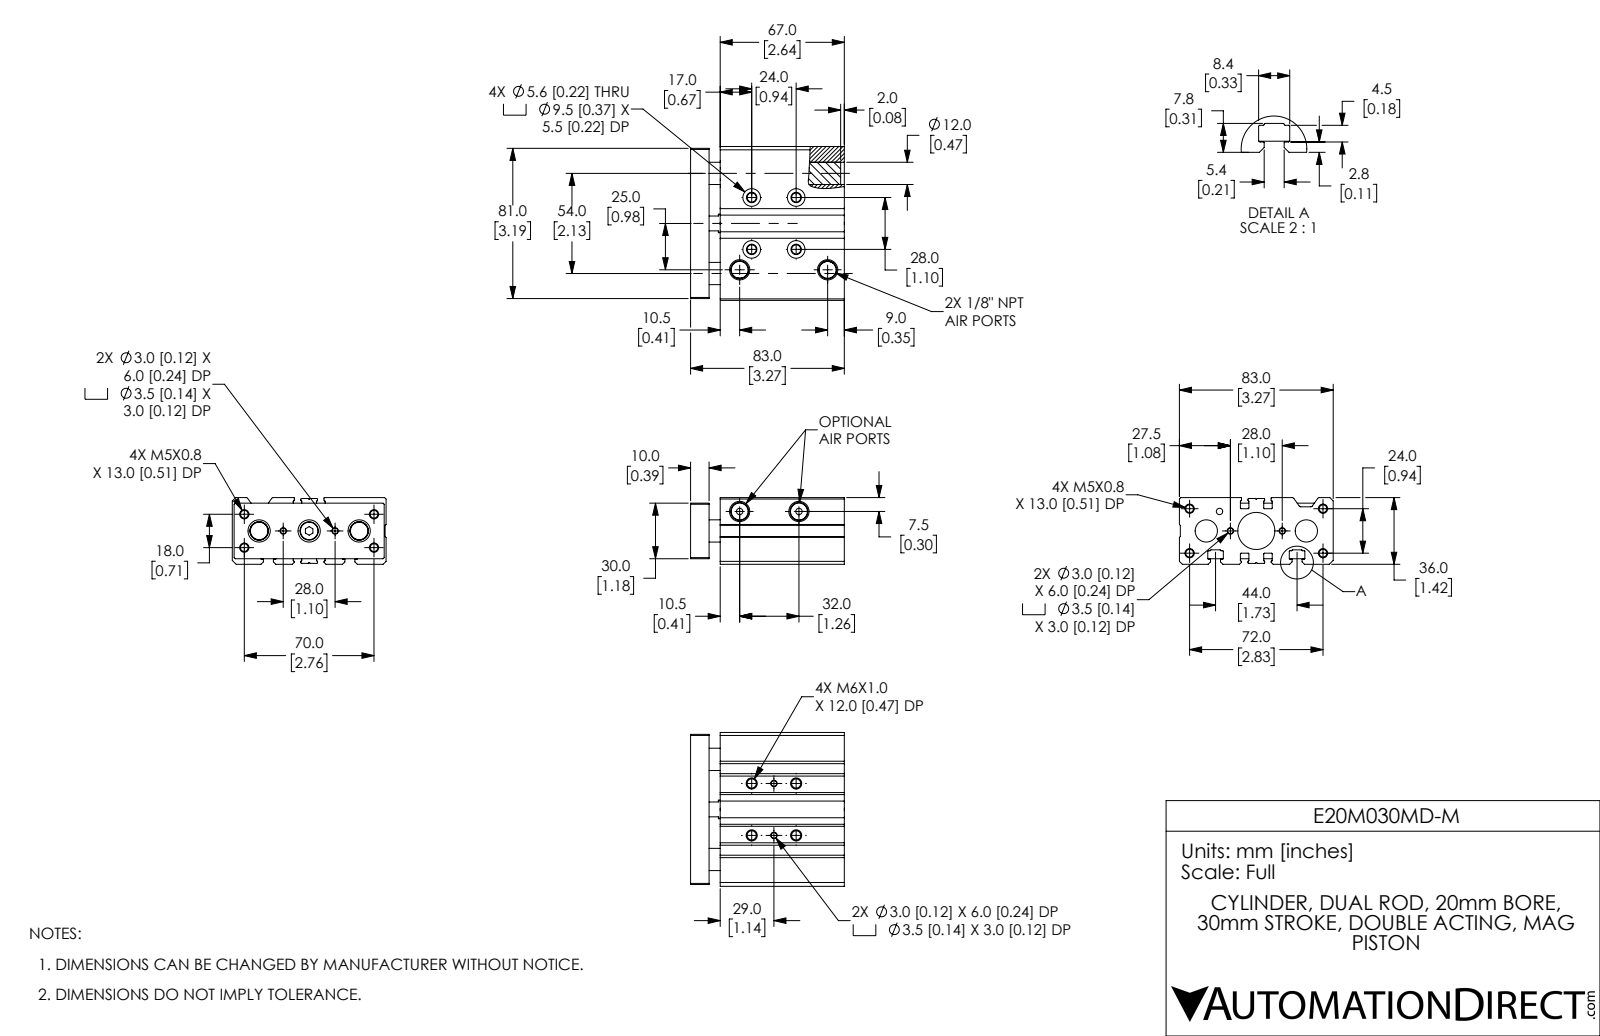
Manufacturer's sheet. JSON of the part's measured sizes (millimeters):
{"part_name": "E20M030MD-M_BODY; E20M030MD-M_ENDPLATE; E20M030MD-M", "step_written_by": "SolidWorks 2019 (CONFIG_CONTROL_DESIGN)", "units": "millimeters", "bodies": {"solids": 5, "faces": 404, "planar": 128, "cylindrical": 182, "other": 94}, "overall_size": [83, 83, 36], "volume_mm3": 189562, "surface_area_mm2": 60022, "round_holes": [[4.13, 8], [3, 4], [3.5, 4], [4.92, 4], [5.6, 4], [9.5, 4], [6, 3], [12, 3], [3.43, 2], [9.91, 2], [3.43, 1], [12, 1]], "round_bosses_or_shafts": [[10, 1], [9.91, 1]], "partial_cylinders_radius": [[0.4, 20], [0.2, 18], [0.3, 10], [0.25, 8], [1, 4]], "face_to_face_distances": [83, 6, 3, 36, 0.5, 16, 73, 30, 67, 10], "hole_center_spacings": [3.16, 12, 12.04, 15, 21.02, 22.85, 24, 25.06]}
